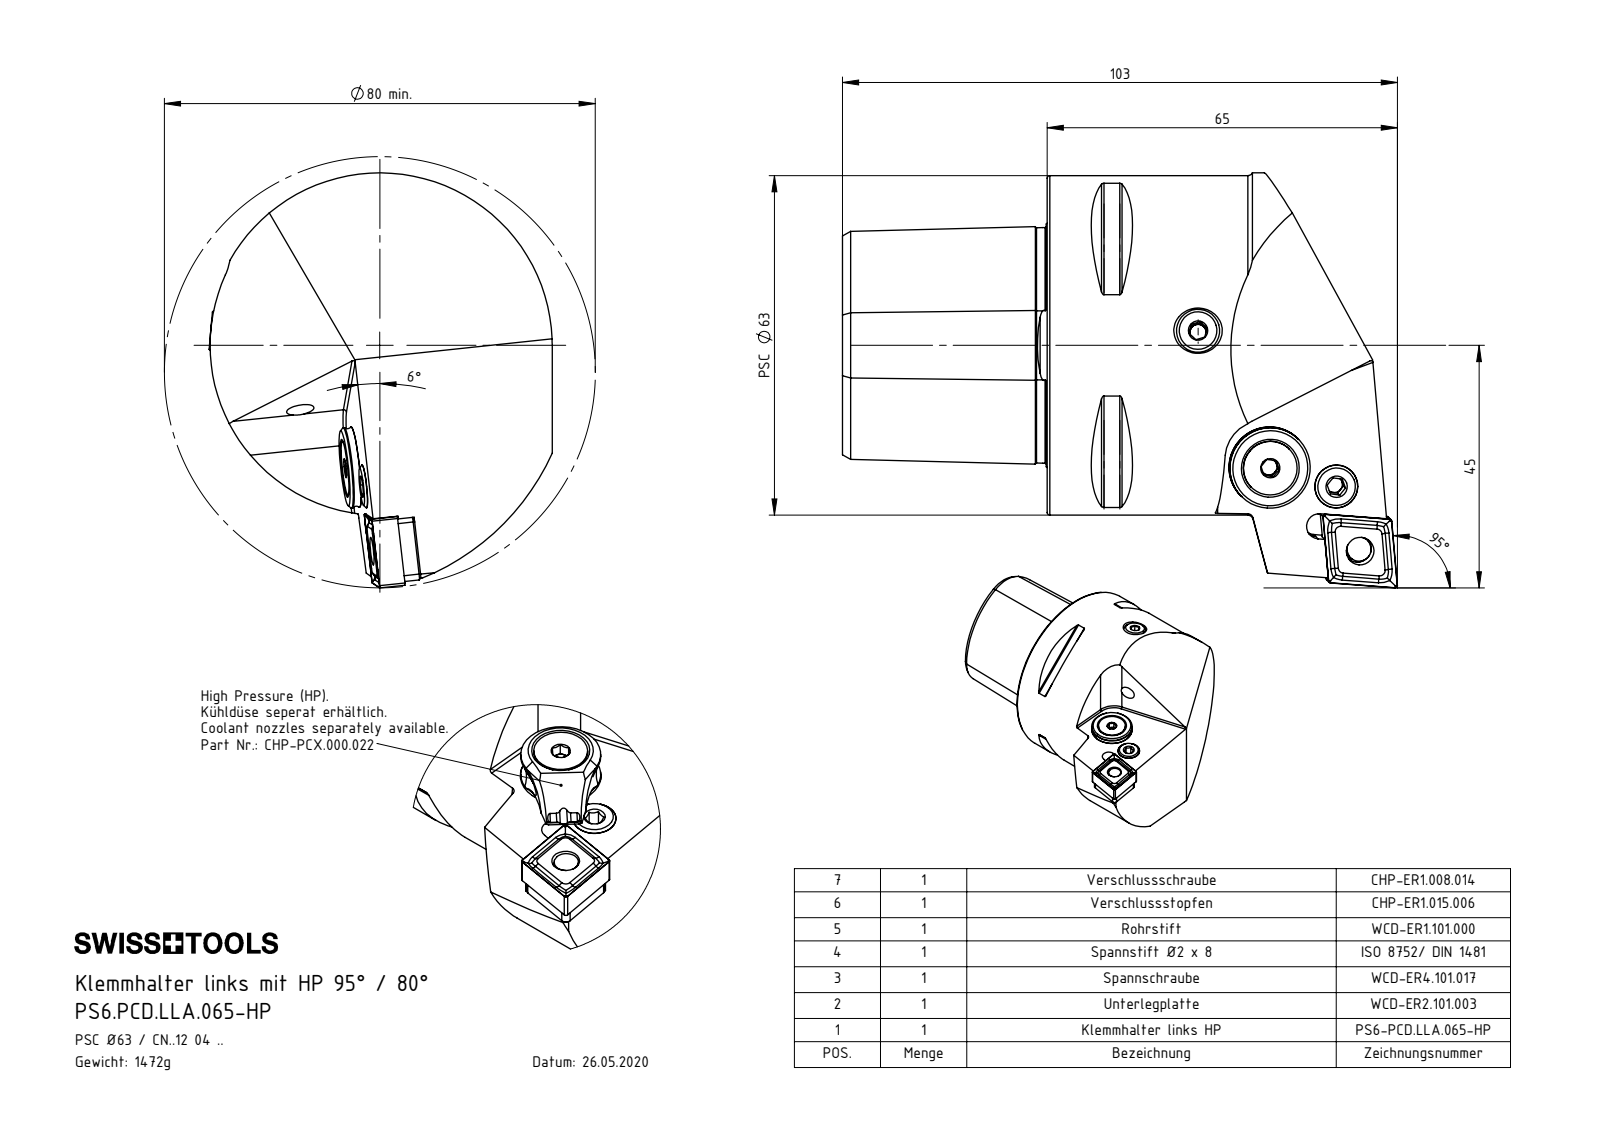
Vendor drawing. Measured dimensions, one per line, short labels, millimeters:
name: WCD-ER1.101.000; DIN 7991 - M5x15; WCD-ER2.101.003_A; WCD-ER3.101.000_A (+8 more)
written by: SolidWorks 2017 (AUTOMOTIVE_DESIGN)
unit: mm
bodies: 11 solids, 444 faces (133 planar, 112 cylindrical, 199 other)
size: 103 × 77 × 63.69
volume: 186 989 mm³; area: 34 332 mm²
holes: 2× ⌀4.2, 2× ⌀5, 2× ⌀7, 1× ⌀1.2, 1× ⌀2, 1× ⌀2.5, 1× ⌀3, 1× ⌀4, 1× ⌀5.16, 1× ⌀5.2, 1× ⌀6.4, 1× ⌀8.1
bosses: 2× ⌀8, 1× ⌀63, 1× ⌀15, 1× ⌀13.4, 1× ⌀10, 1× ⌀7.9, 1× ⌀6.4, 1× ⌀5.5
rounds: 10× R0.5, 4× R0.4, 4× R1, 2× R2.5, 1× R2.1, 1× R2.2, 1× R2.35, 1× R2.8
face distances: 38, 24.88, 4.5, 27, 11, 4.46, 55.8, 11.8, 3.14, 3.18
hole spacings: 4.51, 8.73, 13.08, 19.87, 23.12, 12.79, 12.85, 19.81
